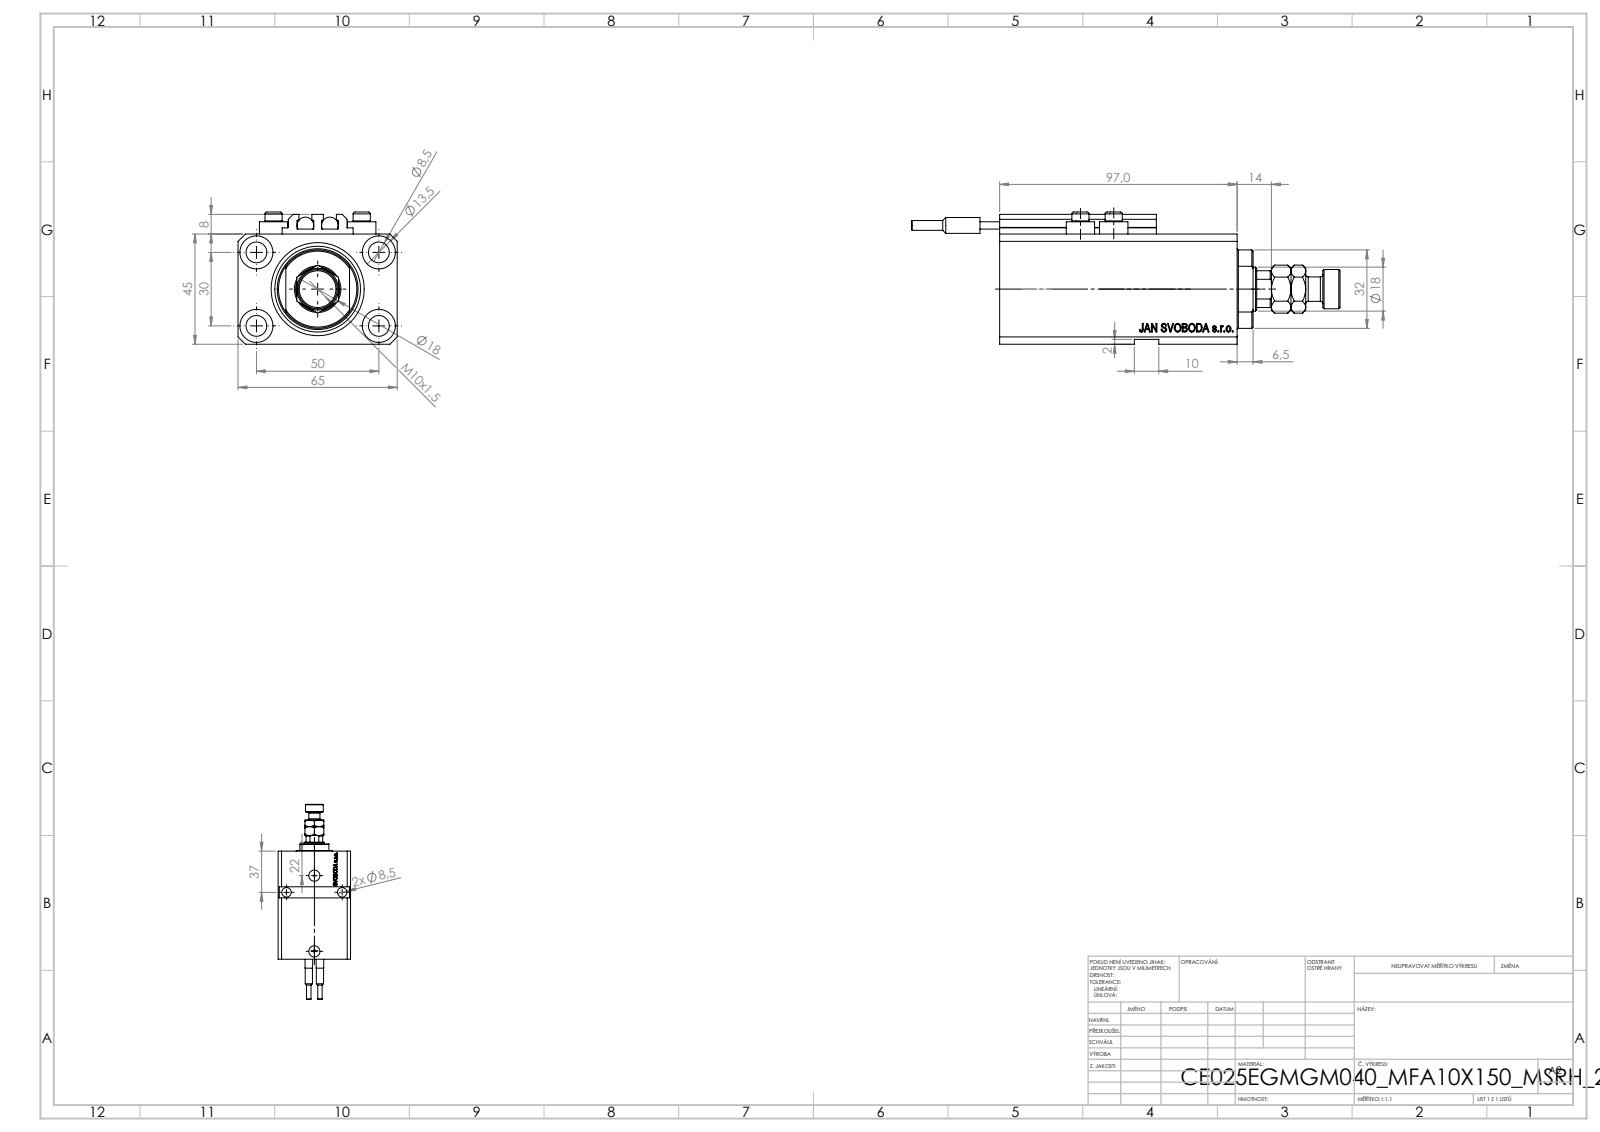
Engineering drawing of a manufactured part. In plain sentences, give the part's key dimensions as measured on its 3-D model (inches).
The part is named "V250CE_VC_E; V250CE_C_VCP; SWITCH_V250CE; MFA (+2 more)". Its 3-D file was written by "SolidWorks 2019 (CONFIG_CONTROL_DESIGN)". It is 11 solids with 1171 faces: 559 planar, 142 cylindrical and 470 other. Overall it measures 6.89 by 2.559 by 2.126 inches. Its volume is 15.88 cubic inches and its surface area 116.4 square inches. Round holes: 7 of diameter 0.335, 4 of diameter 0.049, 4 of diameter 0.157, 4 of diameter 0.531, 2 of diameter 0.394, 2 of diameter 0.518, 2 of diameter 0.787, 1 of diameter 0.709, 1 of diameter 0.984, 1 of diameter 1.496. Round bosses or shafts: 4 of diameter 0.457, 4 of diameter 0.276, 2 of diameter 0.268, 2 of diameter 0.256, 2 of diameter 0.157, 1 of diameter 0.63, 1 of diameter 0.394. Partial cylindrical surfaces (rounded edges, fillets, slot ends): 10 of radius 0.008, 1 of radius 0.335, 1 of radius 0.63. The main face-to-face distances are 1.772, 2.559, 0.551, 0.079, 1.85, 3.268, 0.118, 3.819, 0.272, 0.197. The hole center spacings are 1.148, 1.969, 0.535, 0.595, 1.098, 1.181, 1.228, 1.245.
